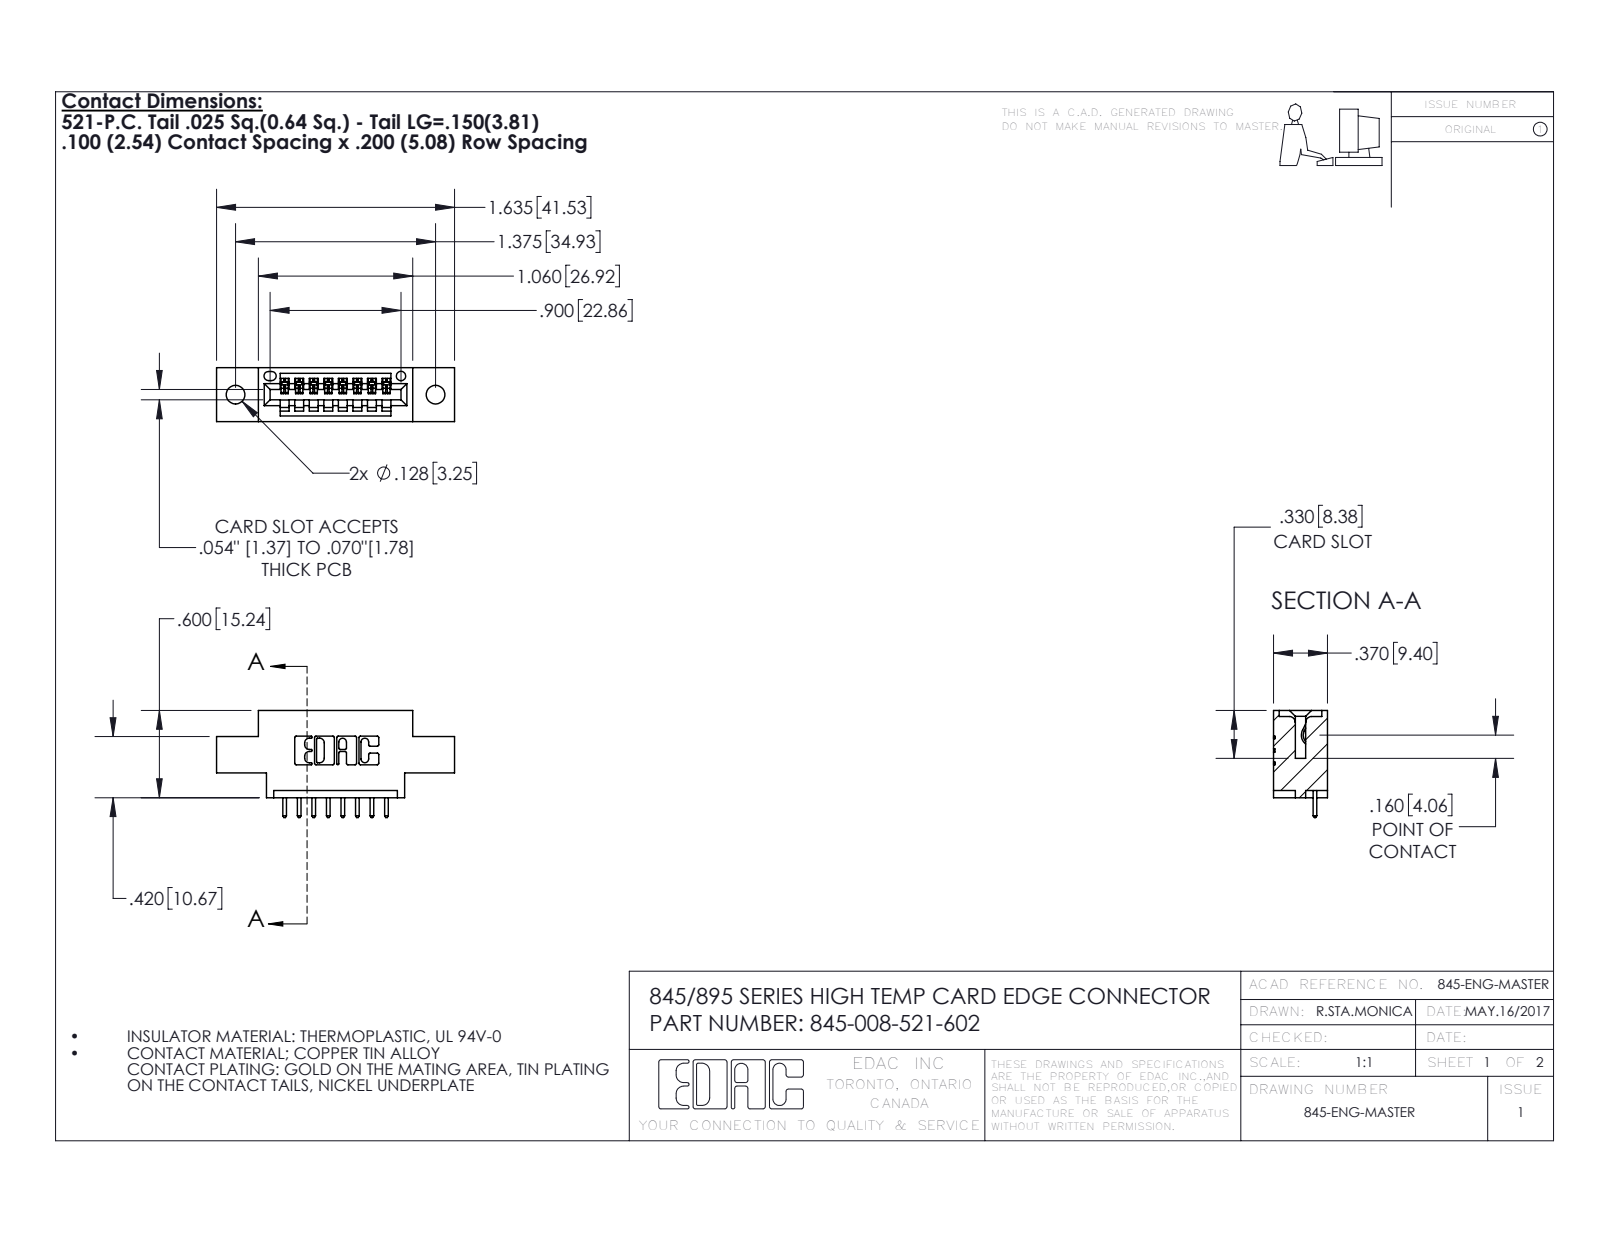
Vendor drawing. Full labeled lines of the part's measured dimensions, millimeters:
Part name (STEP PRODUCT): 345-008-521-602; 345 Part_0.170 Offset - 0.128 Dia; 345-292-001_345-293-121
STEP written by: SolidWorks 2016 (CONFIG_CONTROL_DESIGN)
Units: millimetres
Bodies: 9 solids, 594 faces (404 planar, 190 cylindrical, 0 other)
Overall size (bounding box): 41.5 × 18.7 × 10
Volume: 3 420 mm³ · Surface area: 3 987 mm²
Round holes (diameter × count): ⌀3.3 ×2, ⌀1.6 ×1
Partial cylindrical surfaces — rounded edges, fillets, slot ends (radius × count): R0.3 ×22, R0.2 ×16, R0.3 ×16, R0.2 ×6, R0.8 ×6, R0.7 ×3, R0.8 ×2, R1 ×2
Main face-to-face distances: 9.4, 5.1, 7.6, 1.8, 2.5, 2.5, 6.9, 0.6, 1.5, 15.2
Hole centre spacings: 6.9, 29.1, 34.9
